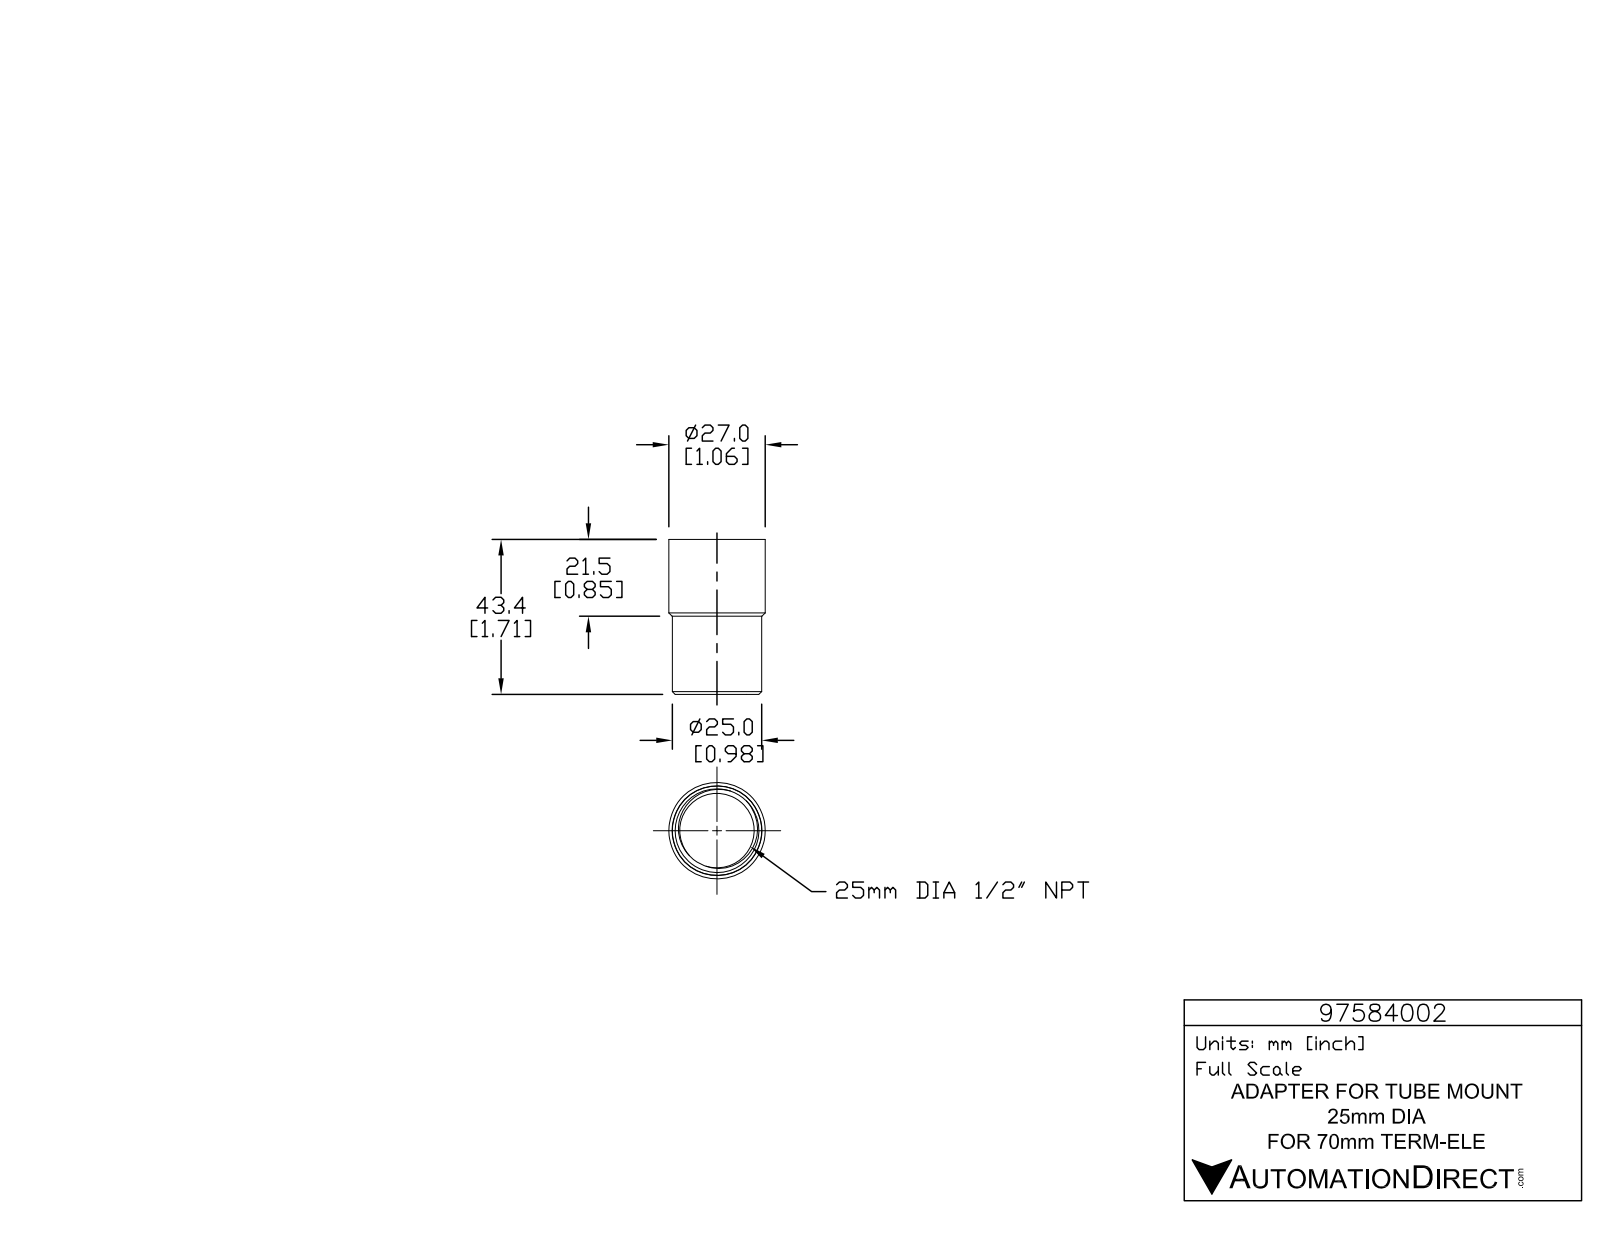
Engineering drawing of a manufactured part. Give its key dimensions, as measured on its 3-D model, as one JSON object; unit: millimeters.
{"part_name": "97584002", "step_written_by": "SolidWorks 2015 (AUTOMOTIVE_DESIGN)", "units": "millimeters", "bodies": {"solids": 1, "faces": 66, "planar": 5, "cylindrical": 54, "other": 7}, "overall_size": [43.3, 27, 27], "volume_mm3": 6330, "surface_area_mm2": 9355, "round_holes": [[23.4, 1]], "round_bosses_or_shafts": [[27, 1], [25, 1]], "face_to_face_distances": [43.4, 21.9, 21.5]}
